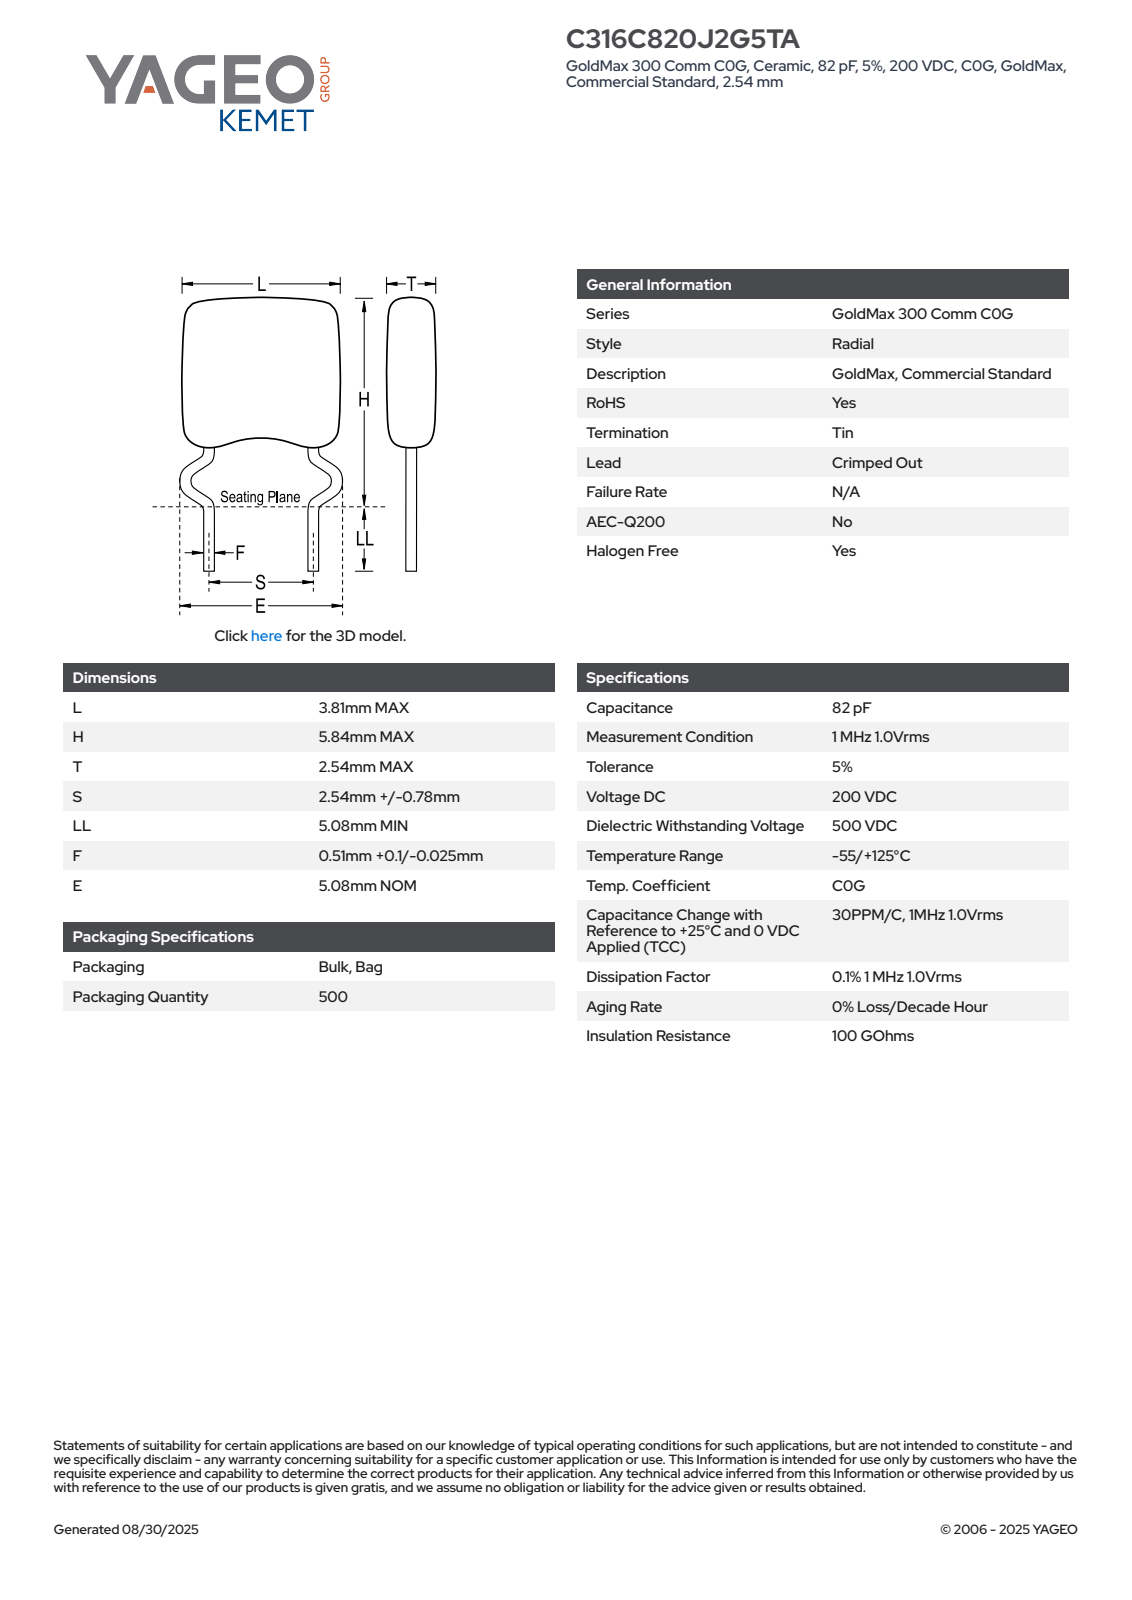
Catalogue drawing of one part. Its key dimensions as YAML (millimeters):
part_name: "CCR_RCCR_C316_L3.81H5.84T2.54S2.54LL5.08F0.51E5.08"
step_written_by: "SolidWorks 2014 (AUTOMOTIVE_DESIGN)"
units: millimeters
bodies: {solids: 4, faces: 104, planar: 66, cylindrical: 16, other: 22}
overall_size: [10.92, 5.08, 2.54]
volume: 36
surface_area: 87
round_bosses_or_shafts:
  - {diameter: 0.51, count: 2}
partial_cylinders:
  - {radius: 0.2, count: 8}
  - {radius: 0.75, count: 4}
face_to_face_distances: [2.54, 3.81, 3.68, 7.24, 10.92, 0.61, 1.49, 9.34, 2.1, 1.58]
